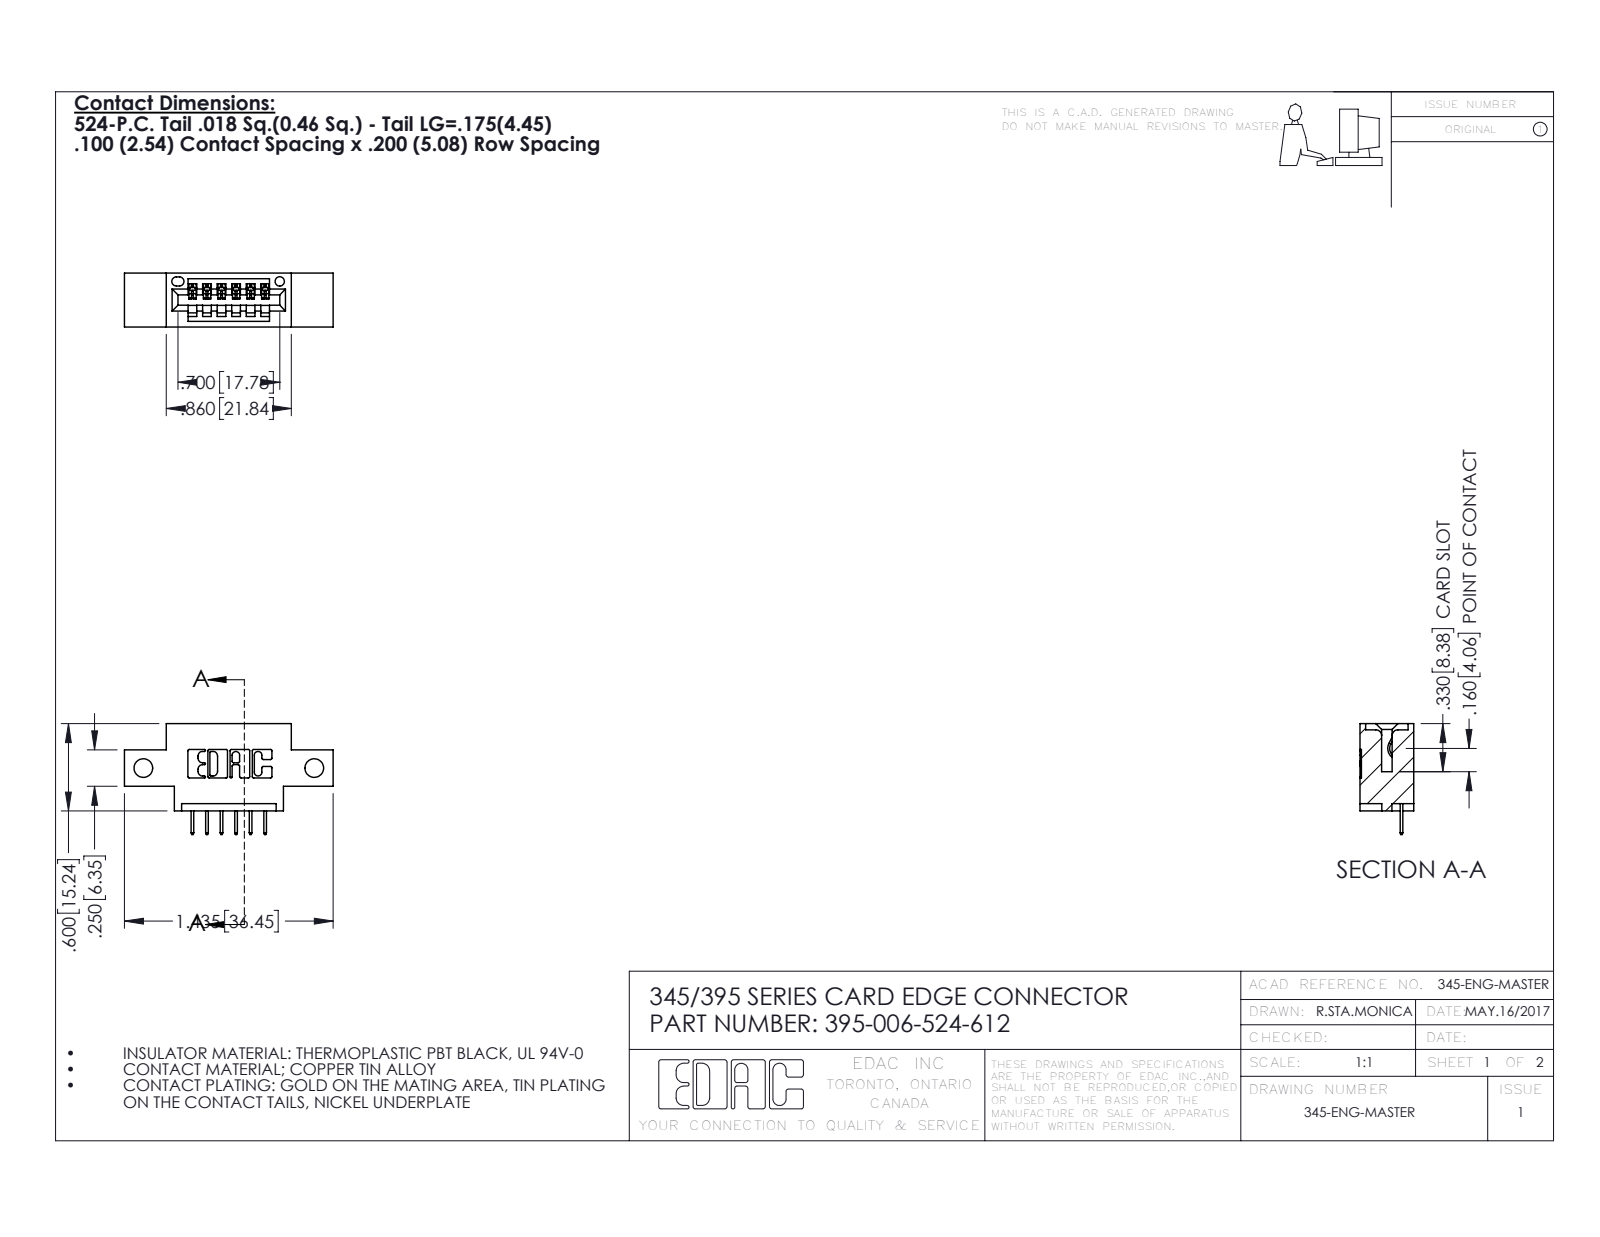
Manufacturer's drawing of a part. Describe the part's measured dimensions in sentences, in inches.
The part is named "345 Part_0.170 Offset - Side Mount; 395-006-524-612; 345-292-001_345-293-124". Its 3-D file was written by "SolidWorks 2016 (CONFIG_CONTROL_DESIGN)". It is 7 solids with 502 faces: 360 planar, 142 cylindrical and 0 other. Overall it measures 1.435 by 0.762 by 0.37 inches. Its volume is 0.18 cubic inches and its surface area 5.162 square inches. Round holes: 2 of diameter 0.128, 1 of diameter 0.064. Partial cylindrical surfaces (rounded edges, fillets, slot ends): 22 of radius 0.01, 12 of radius 0.006, 6 of radius 0.007, 6 of radius 0.031, 3 of radius 0.026, 2 of radius 0.031, 2 of radius 0.04, 1 of radius 0.014. The main face-to-face distances are 0.37, 0.2, 0.1, 0.072, 0.298, 0.25, 0.06, 0.3, 0.025, 0.098. The hole center spacings are 1.175.
